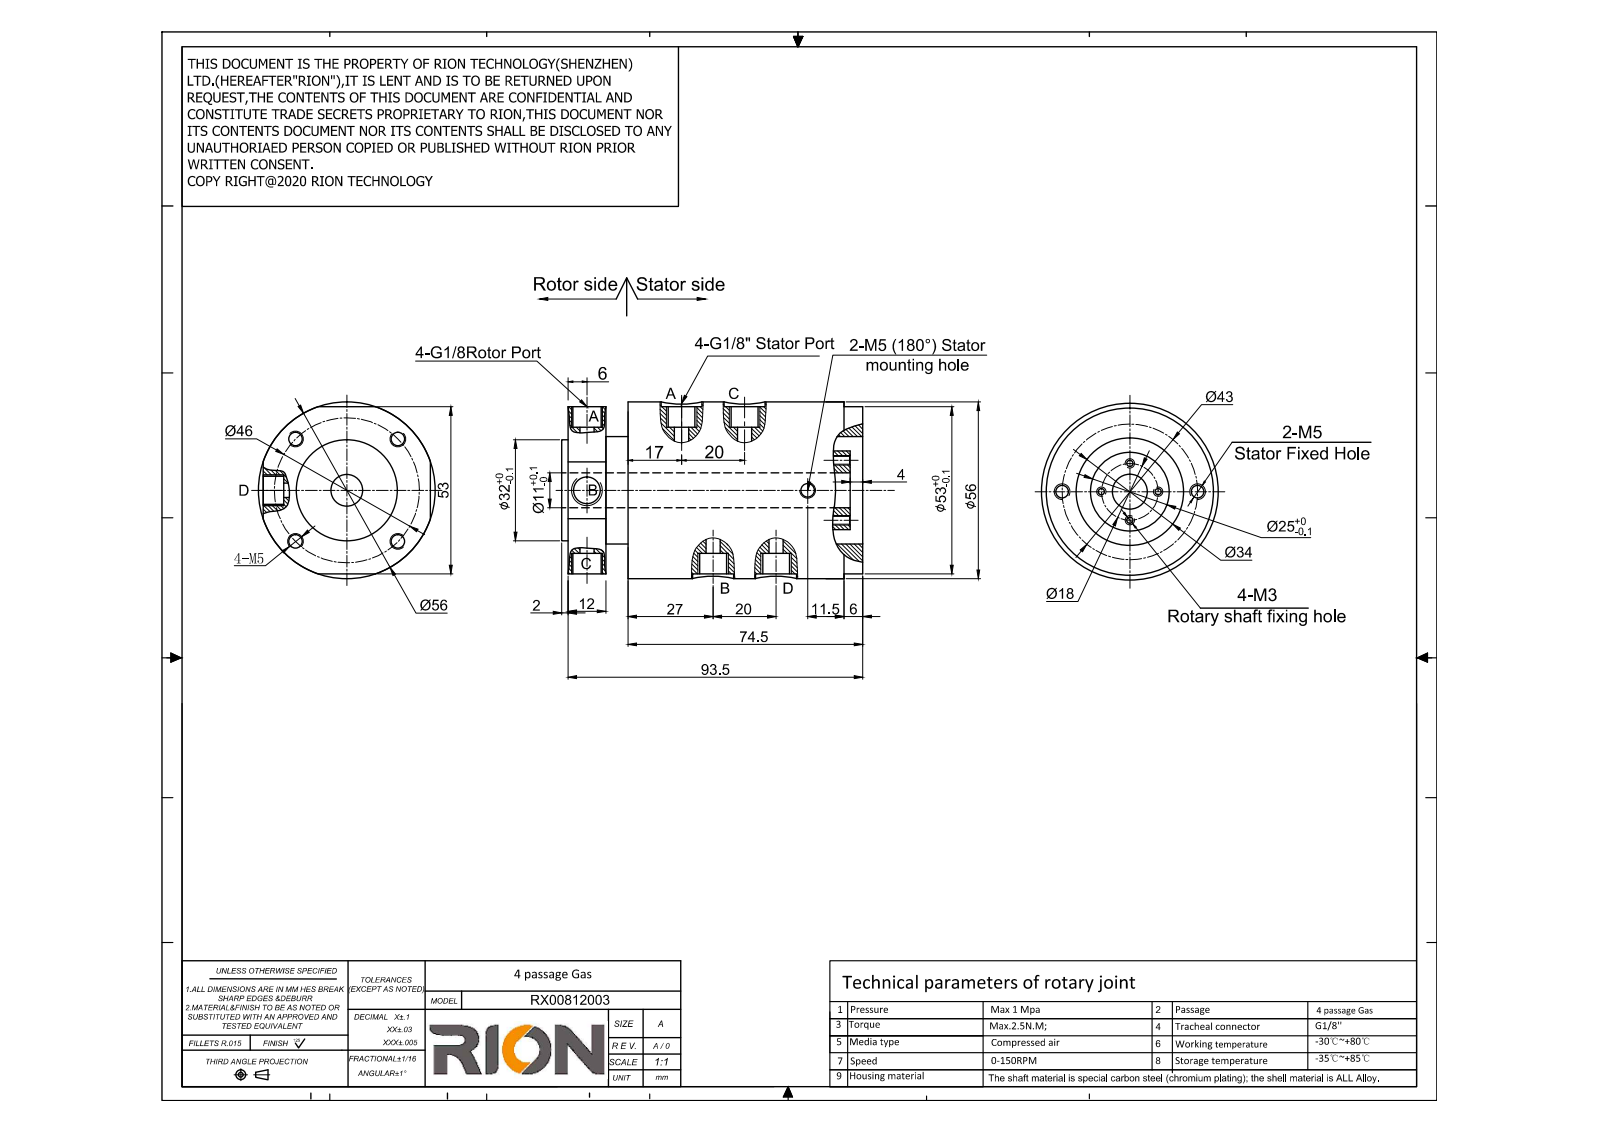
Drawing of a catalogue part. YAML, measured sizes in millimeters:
part_name: "RX00812003--RQ400F-01"
step_written_by: "SolidWorks 2014 (CONFIG_CONTROL_DESIGN)"
units: millimeters
bodies: {solids: 1, faces: 117, planar: 25, cylindrical: 60, other: 32}
overall_size: [95.5, 56, 56]
volume: 196844
surface_area: 32095
round_holes:
  - {diameter: 4.2, count: 7}
  - {diameter: 8.8, count: 6}
  - {diameter: 2.5, count: 4}
  - {diameter: 11, count: 1}
  - {diameter: 25.4, count: 1}
  - {diameter: 34, count: 1}
round_bosses_or_shafts:
  - {diameter: 56, count: 1}
  - {diameter: 53, count: 1}
  - {diameter: 32, count: 1}
  - {diameter: 25, count: 1}
face_to_face_distances: [19, 7, 12, 74.5, 93.5, 81.5, 2, 21, 14, 95.5]
hole_center_spacings: [17.81, 30.04, 9, 12.73, 17.08, 23, 23.31, 32.52]
